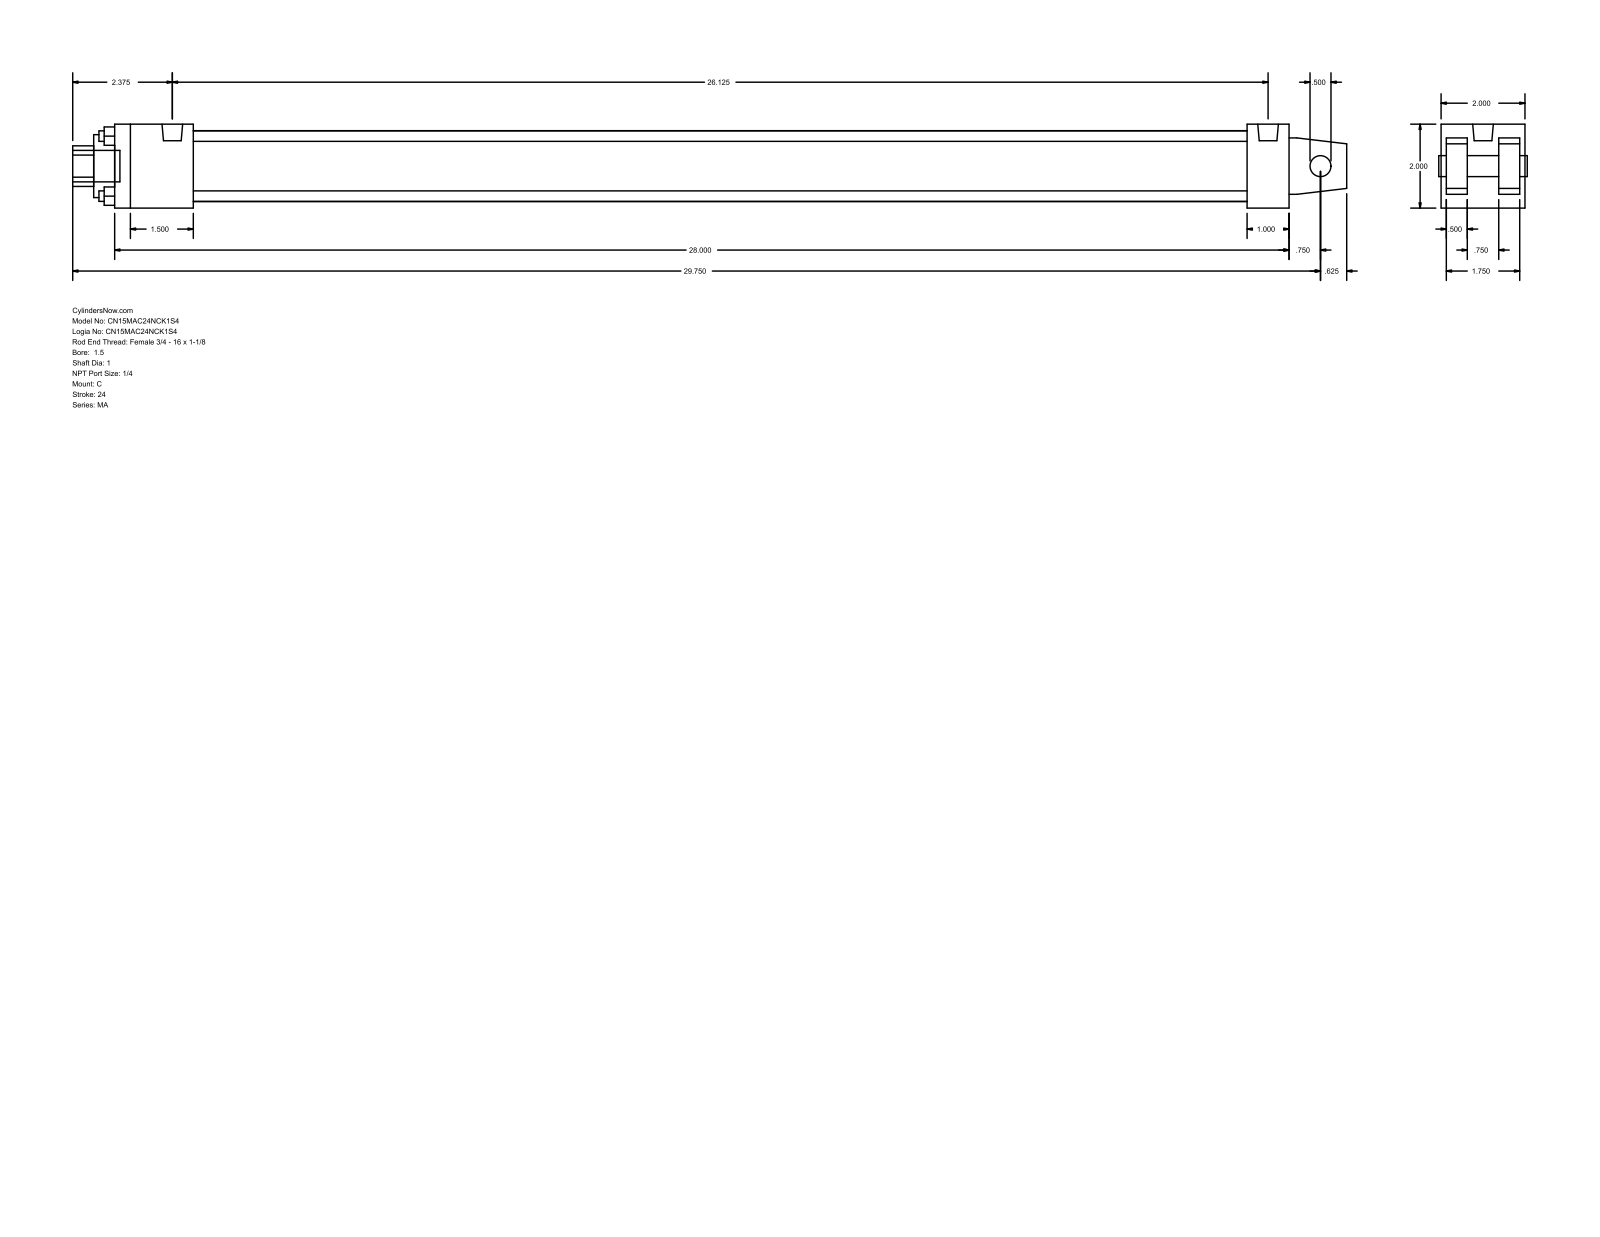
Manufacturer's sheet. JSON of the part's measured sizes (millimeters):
{"part_name": "MA_C__0150_1", "step_written_by": "GSSL Pune (CONFIG_CONTROL_DESIGN)", "units": "millimeters", "bodies": {"solids": 0, "faces": 103, "planar": 76, "cylindrical": 27, "other": 0}, "overall_size": [771.52, 50.8, 50.8], "round_holes": [[6.35, 4], [12.7, 1], [25.4, 1], [38.1, 1], [42.93, 1]], "round_bosses_or_shafts": [[7.94, 4], [12.49, 2], [19.05, 1]], "partial_cylinders_radius": [[12.29, 1]], "face_to_face_distances": [50.8, 47.63, 12.7, 3.17, 15.87, 34.93, 31.76, 44.46, 711.2, 25.4], "hole_center_spacings": [25.68, 36.32, 51.36]}
